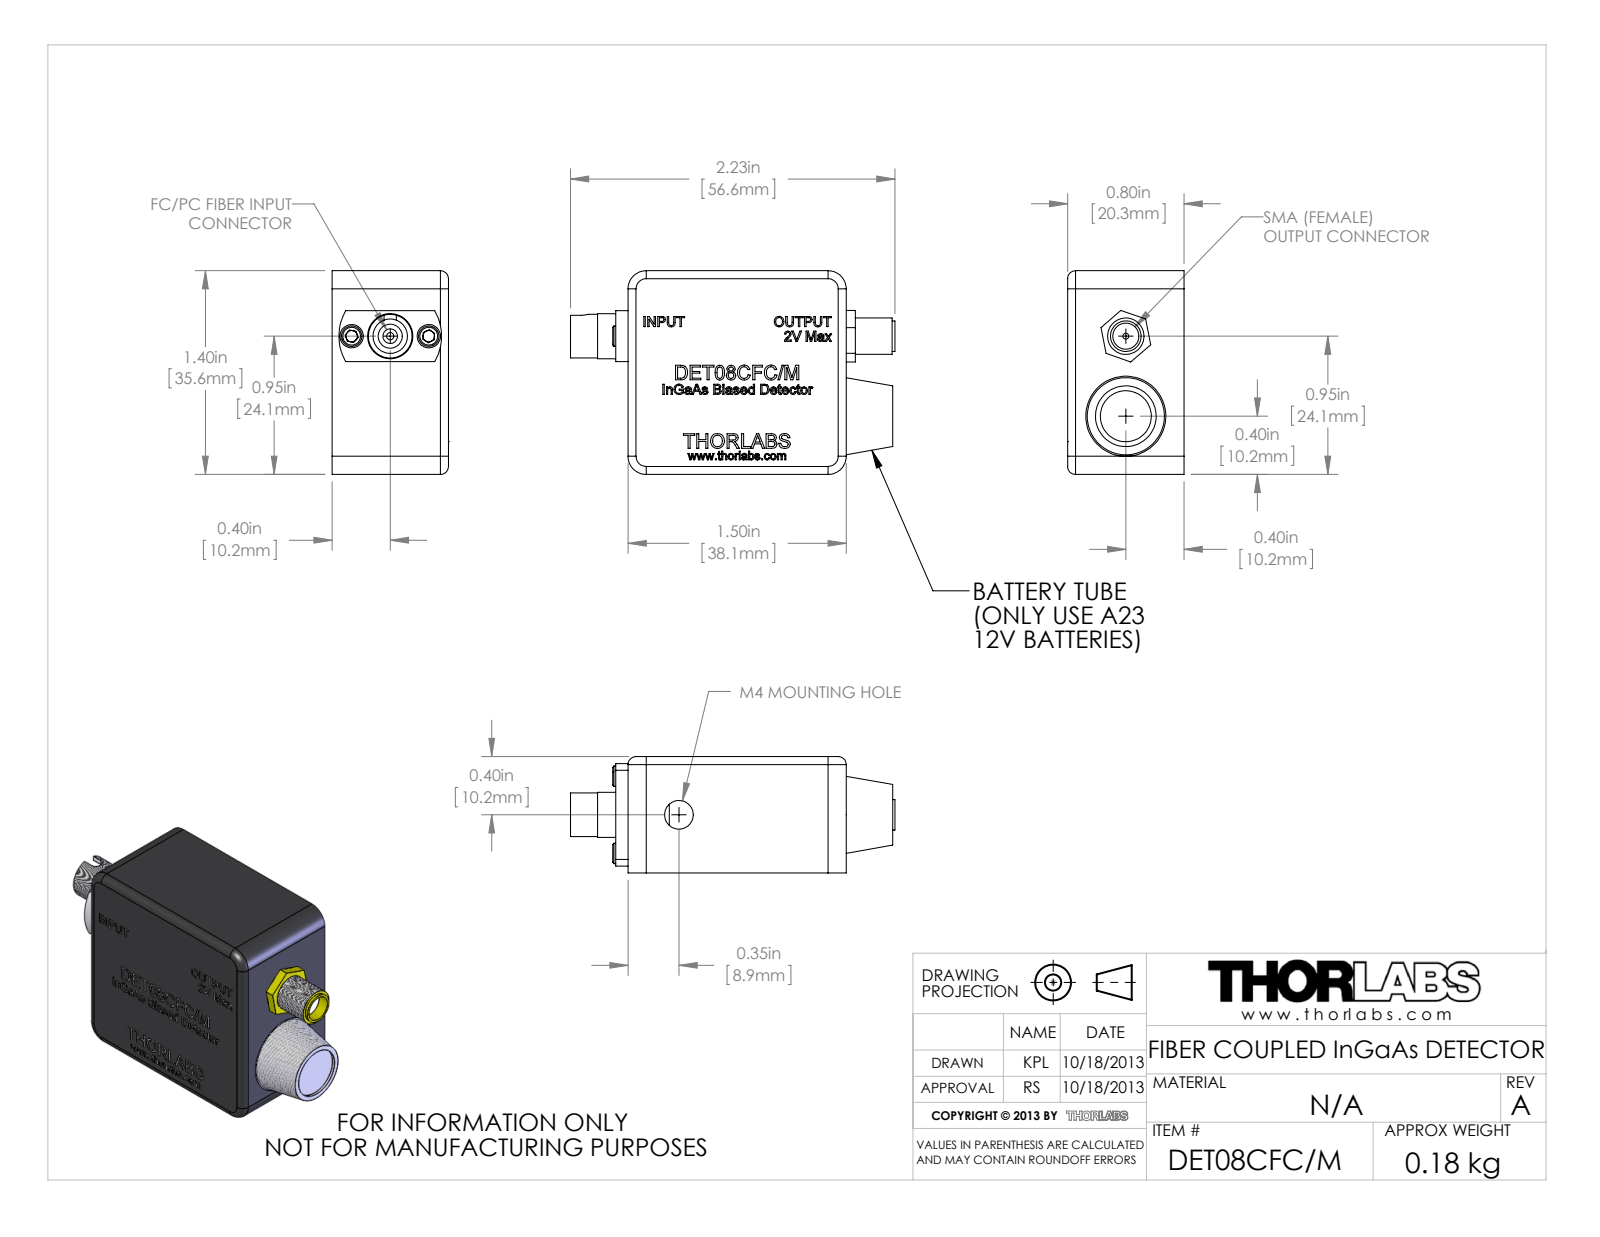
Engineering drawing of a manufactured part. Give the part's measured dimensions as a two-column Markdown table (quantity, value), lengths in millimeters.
| quantity | value |
| --- | --- |
| part name | TTN020144; flat head screw_ai_CR-FHMS 0.086-56x0.188x0.188-N; socket head cap screw_ai_HX-SHCS 0.086-56x0.188x0.188-N; Nut (+5 more) |
| STEP written by | SolidWorks 2012 (AUTOMOTIVE_DESIGN) |
| units | millimeters |
| bodies | 12 solids, 1723 faces (1015 planar, 178 cylindrical, 530 other) |
| overall size | 56.6 × 35.6 × 20.3 |
| volume | 17 550 mm³ |
| surface area | 14 030 mm² |
| round holes (diameter × count) | 1.8 × 6, 2.4 × 4, 3.6 × 4, 3.2 × 3, 2.2 × 2, 4.1 × 2, 0.4 × 1, 1 × 1, 1.3 × 1, 1.3 × 1, 2.5 × 1, 3.2 × 1 |
| round bosses / shafts (diameter × count) | 2.2 × 6, 3.7 × 4, 3.6 × 2, 12 × 1, 11 × 1, 8.3 × 1, 7.9 × 1, 7.6 × 1 |
| partial cylindrical surfaces (radius × count) | 3.2 × 12, 0.8 × 4, 1.4 × 4, 2 × 4, 2.4 × 4, 1.5 × 2, 2.5 × 2, 0.2 × 1 |
| main face-to-face distances | 1.6, 18.7, 20.3, 35.6, 12.7, 14.3, 6, 2.5, 38.1, 33 |
| hole center spacings | 43.1, 29.2, 29.2, 31.8, 31.8, 6.7, 15.5, 22.1 |
